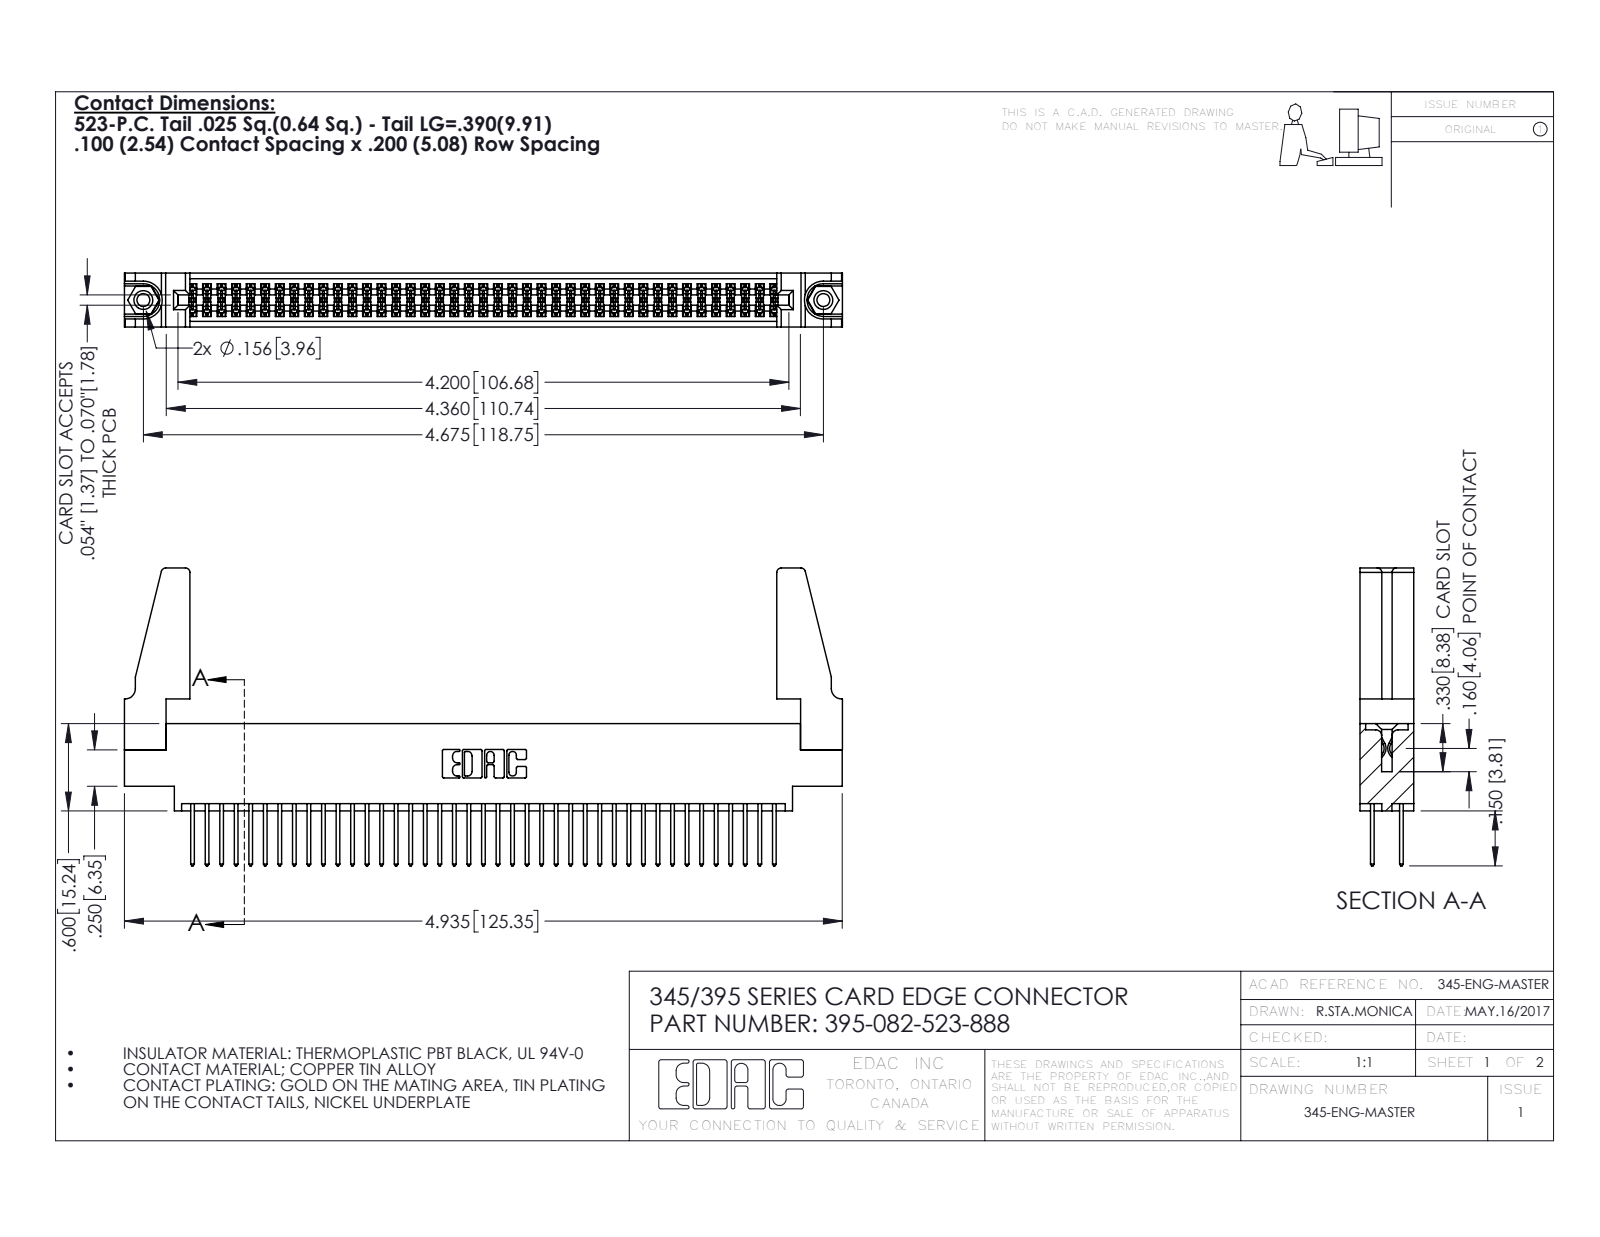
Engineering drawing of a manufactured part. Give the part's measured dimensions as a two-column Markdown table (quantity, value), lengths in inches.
| quantity | value |
| --- | --- |
| part name | 345-220-078_345-220-088; 395-082-523-888; 345-250-001_345-250-001-102; 345 Part_0.170 Offset - 0.156 Dia-TH (+1 more) |
| STEP written by | SolidWorks 2016 (CONFIG_CONTROL_DESIGN) |
| units | inches |
| bodies | 87 solids, 4354 faces (2862 planar, 1476 cylindrical, 16 other) |
| overall size | 4.936 × 2.047 × 0.37 |
| volume | 0.944 in³ |
| surface area | 34.21 in² |
| round holes (diameter × count) | 0.089 × 2, 0.125 × 2, 0.156 × 2, 0.064 × 1 |
| round bosses / shafts (diameter × count) | 0.155 × 2 |
| partial cylindrical surfaces (radius × count) | 0.006 × 123, 0.01 × 82, 0.01 × 22, 0.03 × 8, 0.007 × 6, 0.031 × 6, 0.026 × 3, 0.014 × 2 |
| main face-to-face distances | 0.072, 0.298, 0.37, 0.2, 0.098, 0.272, 0.025, 0.225, 0.175, 0.149 |
| hole center spacings | 0.27, 4.439, 4.675 |
